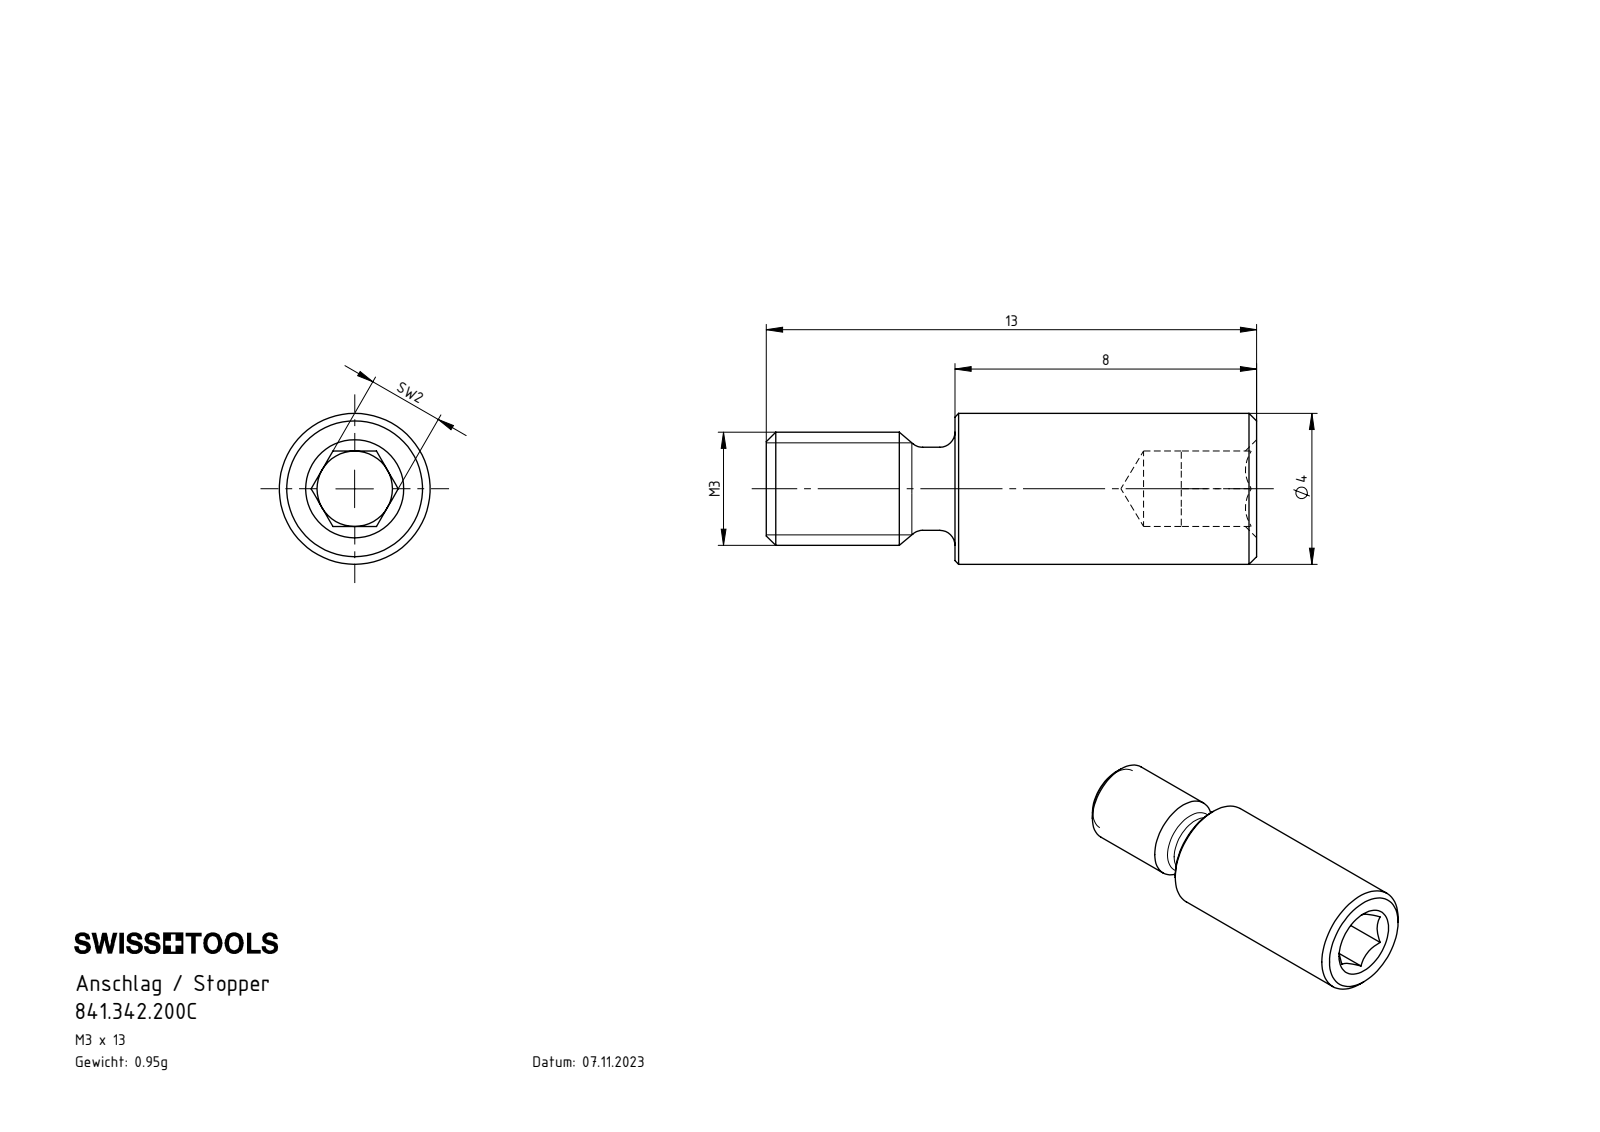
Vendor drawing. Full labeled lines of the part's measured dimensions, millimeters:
Part name (STEP PRODUCT): 841.342.200C
STEP written by: SolidWorks 2022 (AUTOMOTIVE_DESIGN)
Units: millimetres
Bodies: 1 solid, 39 faces (15 planar, 8 cylindrical, 16 other)
Overall size (bounding box): 13 × 4 × 4
Volume: 121 mm³ · Surface area: 189 mm²
Round holes (diameter × count): ⌀2 ×1
Round bosses / shafts (diameter × count): ⌀4 ×1, ⌀3 ×1, ⌀2.2 ×1
Main face-to-face distances: 2, 13, 5, 8, 11, 6
